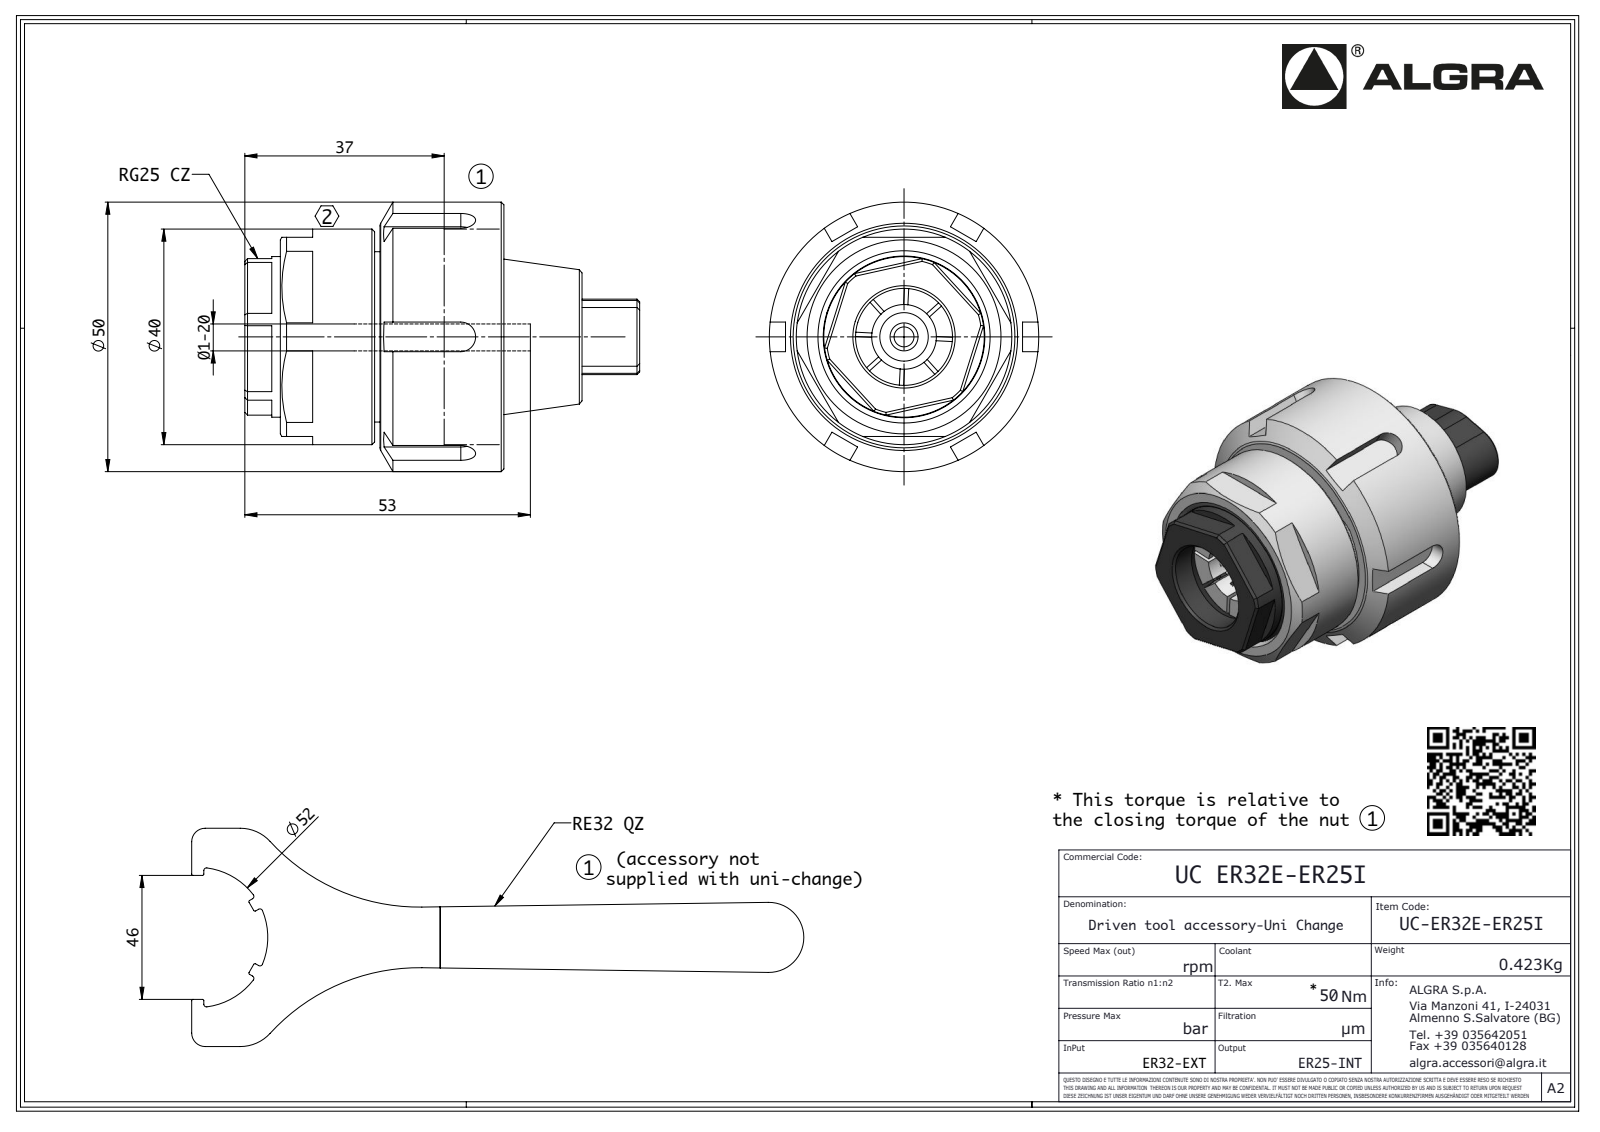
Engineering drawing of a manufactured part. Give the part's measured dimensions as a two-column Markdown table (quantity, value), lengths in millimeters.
| quantity | value |
| --- | --- |
| part name | UCER32E-ER25I |
| STEP written by | SolidWorks 2016 (AUTOMOTIVE_DESIGN) |
| units | millimeters |
| bodies | 1 solid, 382 faces (260 planar, 40 cylindrical, 82 other) |
| overall size | 73.29 × 50 × 50 |
| volume | 79 936 mm³ |
| surface area | 13 150 mm² |
| round holes (diameter × count) | 2.1 × 1 |
| round bosses / shafts (diameter × count) | 50 × 1, 40 × 1, 31.6 × 1, 29.8 × 1, 6.37 × 1, 1.7 × 1 |
| partial cylindrical surfaces (radius × count) | 0.33 × 7, 0.52 × 7, 3.7 × 7, 2.75 × 3, 5.64 × 2, 0.21 × 1, 7 × 1 |
| main face-to-face distances | 48.09, 23, 25.09, 24, 1, 24.09, 41.5, 18.5, 17.5, 6.59 |
